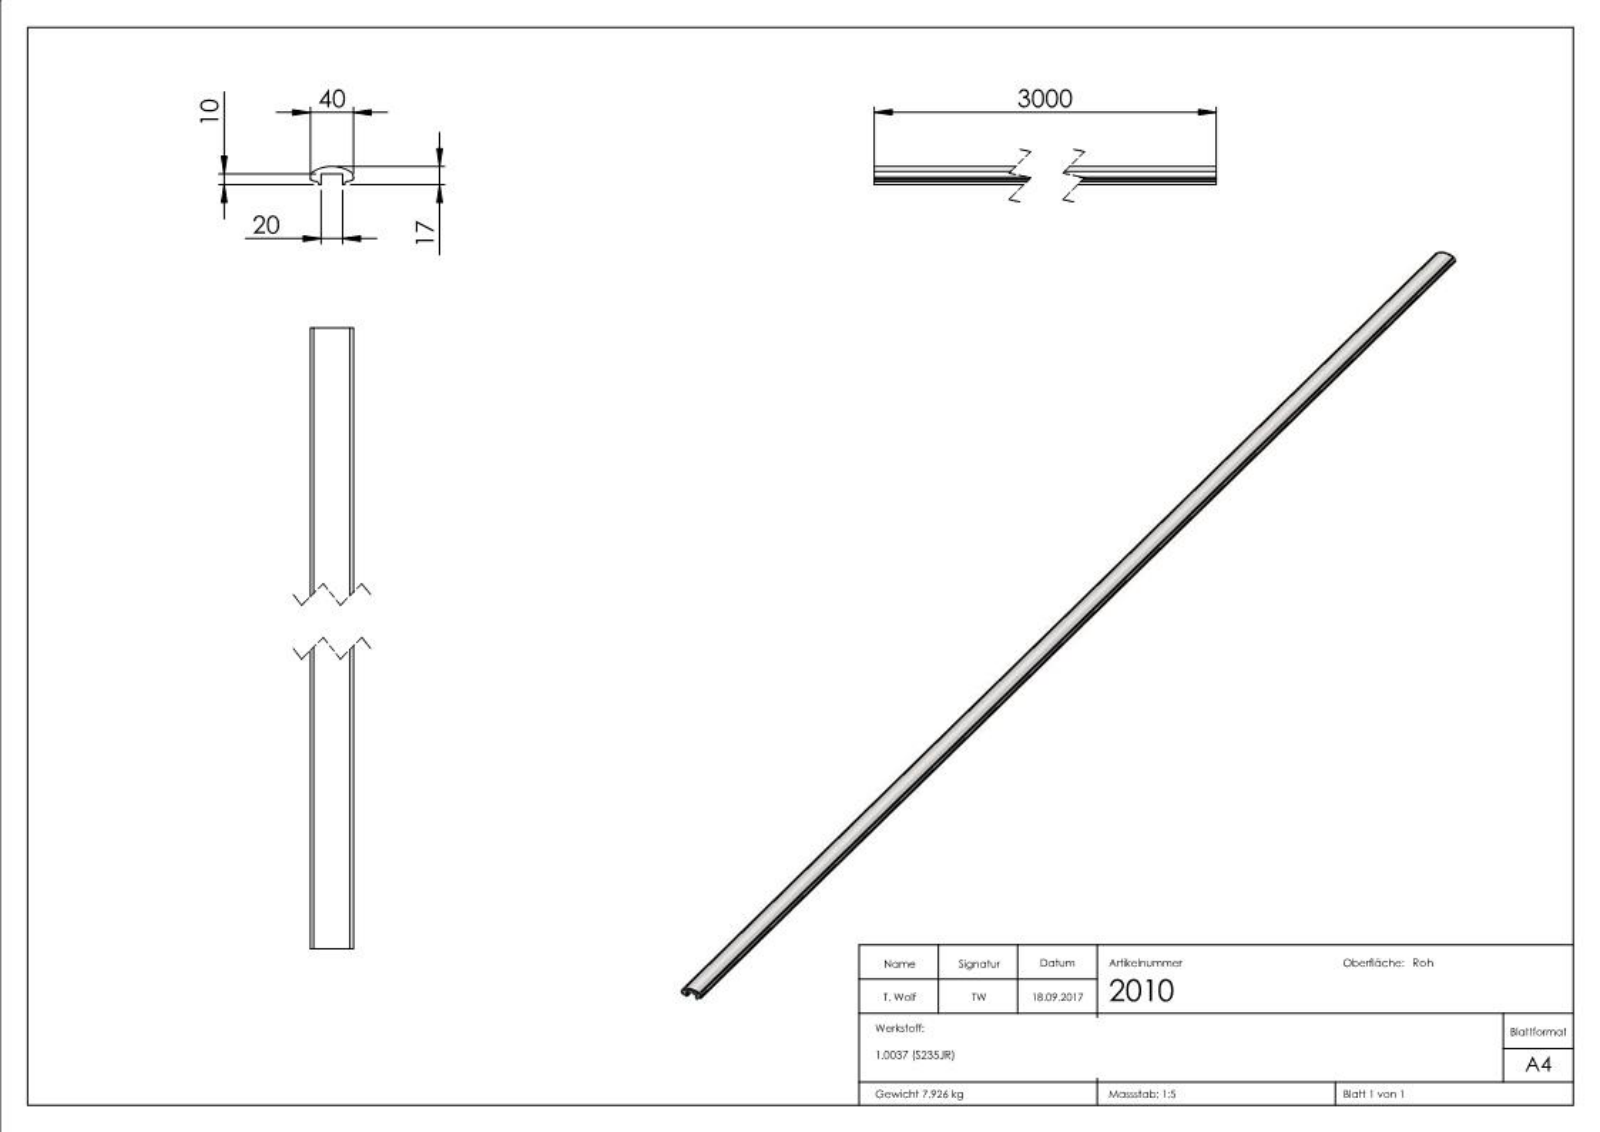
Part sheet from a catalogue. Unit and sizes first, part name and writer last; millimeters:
Units: millimetres
Overall size (bounding box): 3000 × 40 × 17
Partial cylindrical surfaces — rounded edges, fillets, slot ends (radius × count): R1 ×4, R2.81 ×2, R5.81 ×2, R10.39 ×2, R33.28 ×1
Main face-to-face distances: 20, 10, 30, 40, 3000, 10.5, 0.5, 0.39, 2.97, 4.09
Volume: 1 016 000 mm³ · Surface area: 351 930 mm²
Bodies: 1 solid, 134 faces (74 planar, 12 cylindrical, 48 other)
Part name (STEP PRODUCT): 2010
STEP written by: SolidWorks 2015 (CONFIG_CONTROL_DESIGN)
